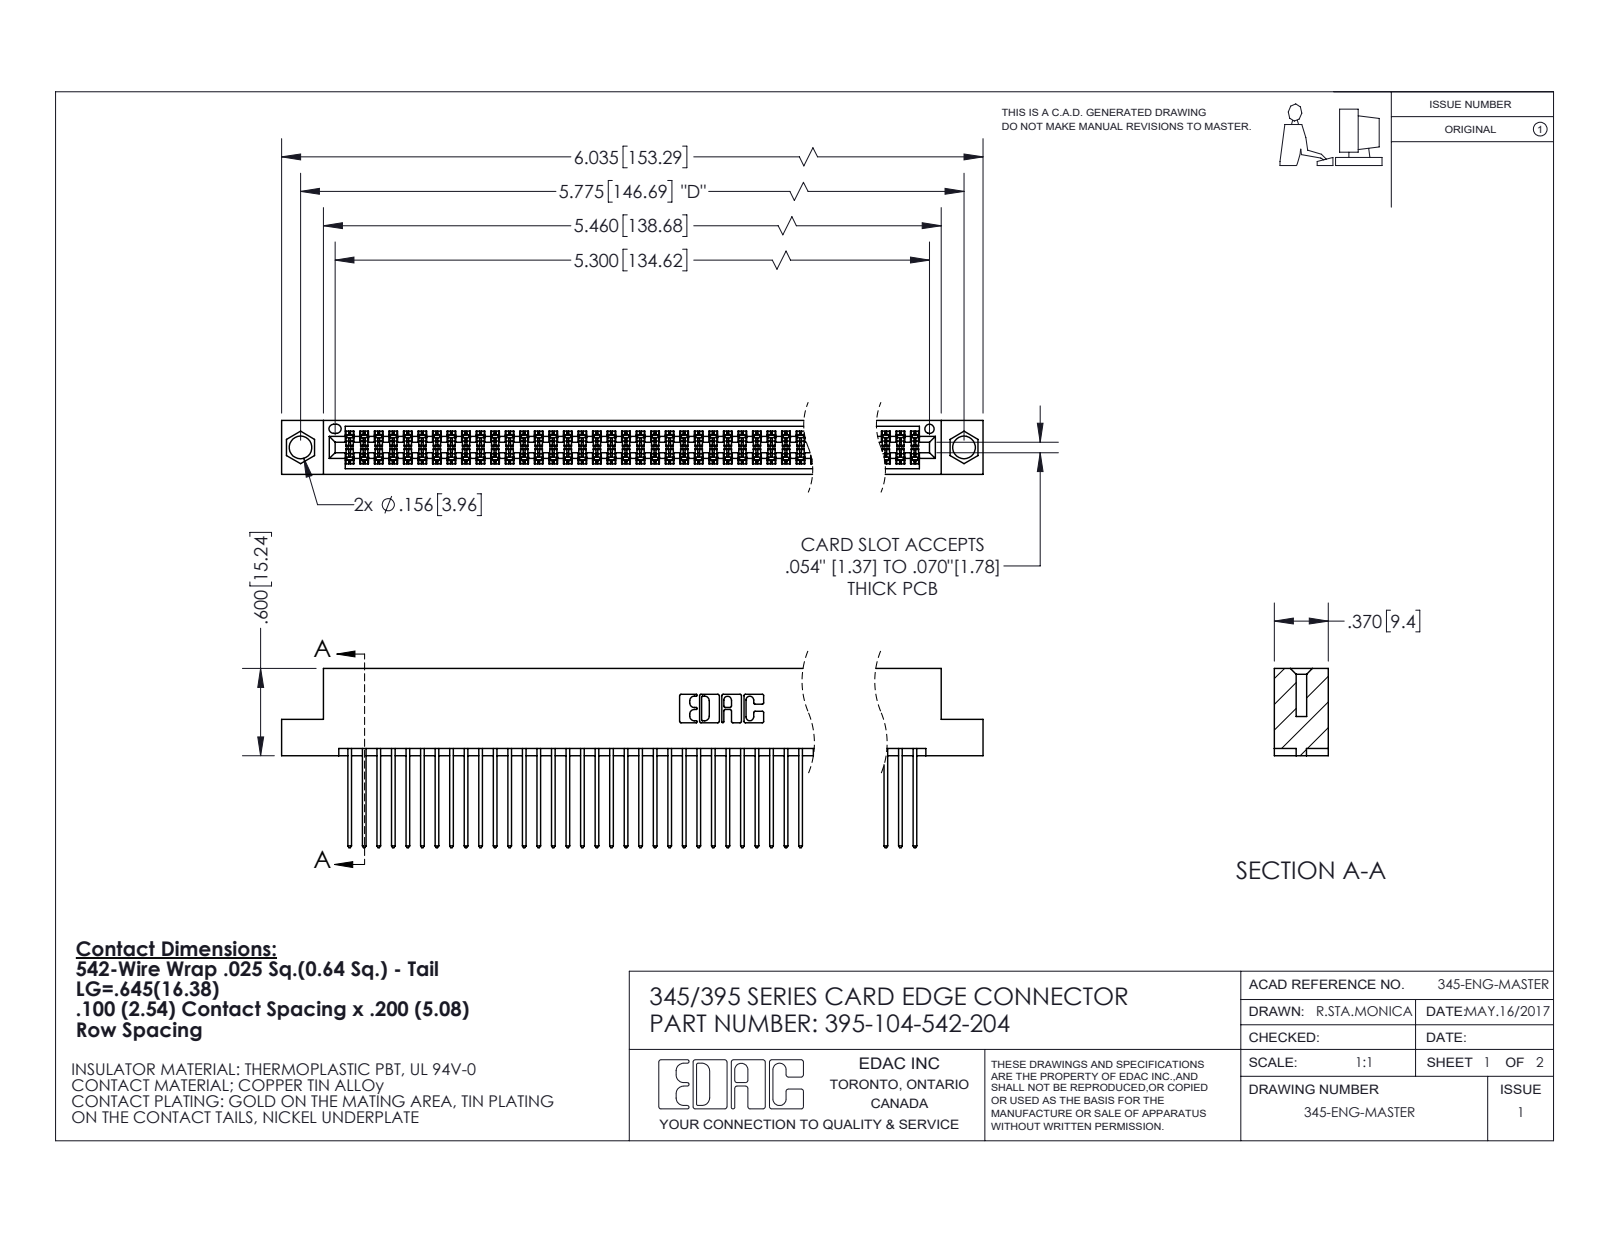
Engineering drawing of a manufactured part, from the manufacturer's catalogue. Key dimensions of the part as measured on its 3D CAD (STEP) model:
Part name (STEP PRODUCT): 345 Part_Flush Mounting Lugs - 0.156 Dia-TI; 345-292-001_345-293-142; 395-104-542-204
STEP written by: SolidWorks 2020 (CONFIG_CONTROL_DESIGN)
Units: inches
Bodies: 105 solids, 5340 faces (3526 planar, 1814 cylindrical, 0 other)
Overall size (bounding box): 6.035 × 1.232 × 0.37
Volume: 0.937 in³ · Surface area: 38.78 in²
Round holes (diameter × count): ⌀0.156 ×2, ⌀0.064 ×1
Partial cylindrical surfaces — rounded edges, fillets, slot ends (radius × count): R0.006 ×156, R0.01 ×104, R0.01 ×22, R0.007 ×6, R0.031 ×6, R0.026 ×3, R0.014 ×2, R0.019 ×2
Main face-to-face distances: 0.072, 0.298, 0.2, 0.098, 0.272, 0.025, 0.225, 0.37, 0.175, 0.149
Hole centre spacings: 0.27, 5.539, 5.775
